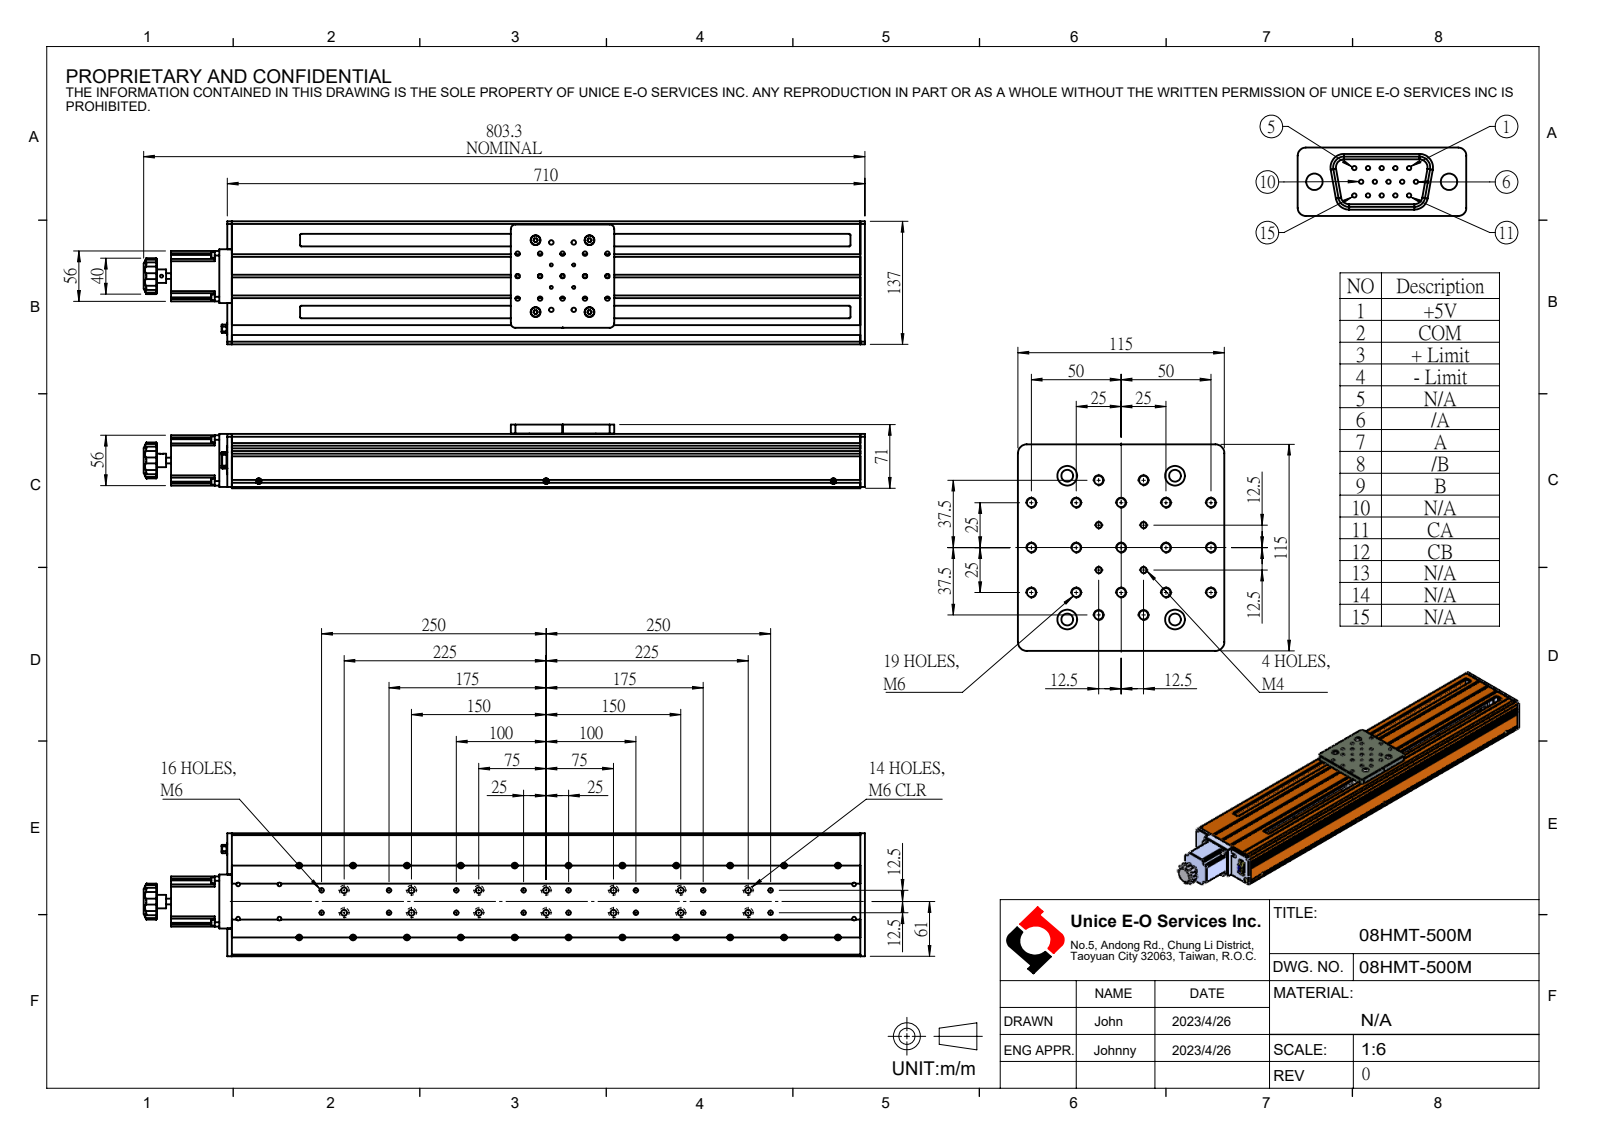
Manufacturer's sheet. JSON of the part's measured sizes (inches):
{"part_name": "08HMT-500M", "step_written_by": "SolidWorks 2022 (CONFIG_CONTROL_DESIGN)", "units": "inches", "bodies": {"solids": 0, "faces": 793, "planar": 349, "cylindrical": 340, "other": 104}, "overall_size": [31.626, 5.394, 2.795], "round_holes": [[0.197, 35], [0.256, 22], [0.433, 16], [0.26, 14], [0.031, 8], [0.13, 6], [0.165, 6], [0.079, 2], [0.089, 2], [0.709, 1], [0.866, 1], [0.984, 1]], "round_bosses_or_shafts": [[0.256, 4], [0.228, 3], [0.303, 2], [0.276, 2], [0.591, 1], [0.551, 1], [0.25, 1]], "partial_cylinders_radius": [[0.059, 8], [0.157, 8], [0.197, 8], [0.292, 8], [0.02, 4], [0.079, 4], [0.177, 4], [0.118, 3]], "face_to_face_distances": [0.079, 2.382, 5.315, 5.236, 0.413, 0.059, 2.323, 5.394, 0.067, 0.354], "hole_center_spacings": [1.556, 0.984, 0.696, 2.201, 1.392, 1.969, 2.509, 2.088]}
